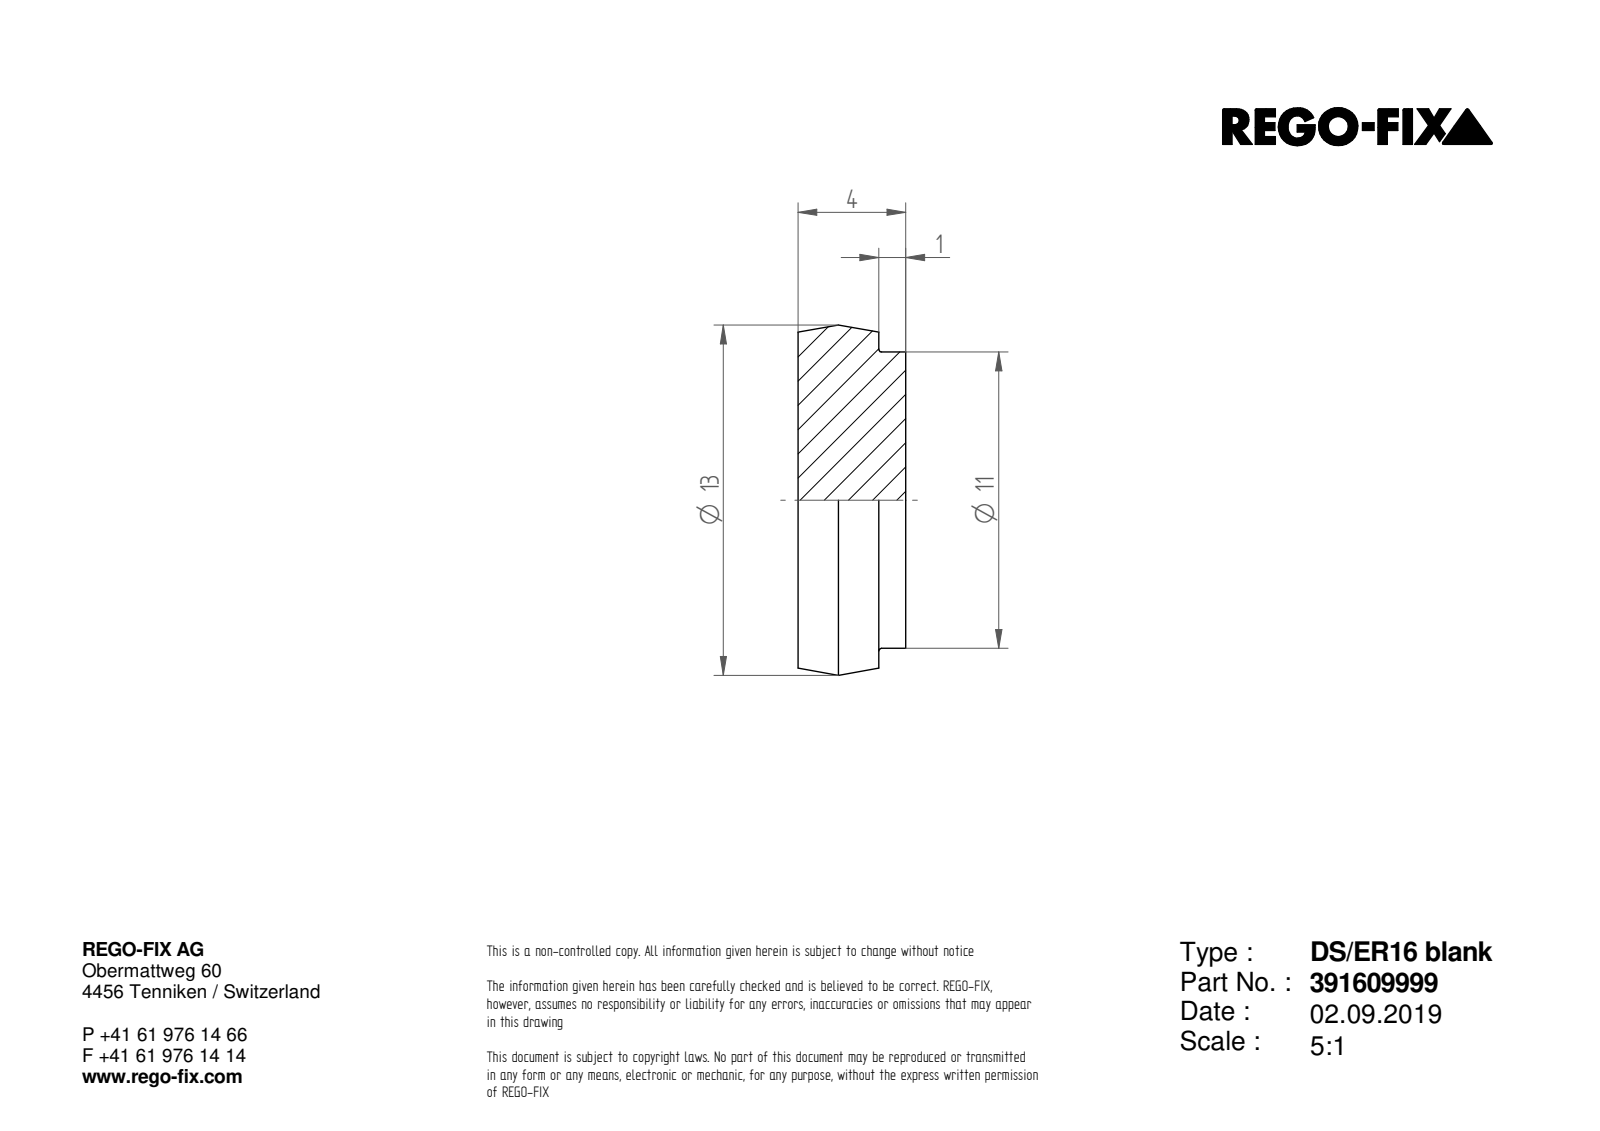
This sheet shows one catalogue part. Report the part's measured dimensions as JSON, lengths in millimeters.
{"part_name": "0019903", "step_written_by": "ST-DEVELOPER v16.7 (AUTOMOTIVE_DESIGN)", "units": "millimeters", "bodies": {"solids": 1, "faces": 7, "planar": 3, "cylindrical": 1, "other": 3}, "overall_size": [13, 13, 4], "volume_mm3": 477, "surface_area_mm2": 399, "round_bosses_or_shafts": [[11, 1]], "face_to_face_distances": [4, 3, 1]}
